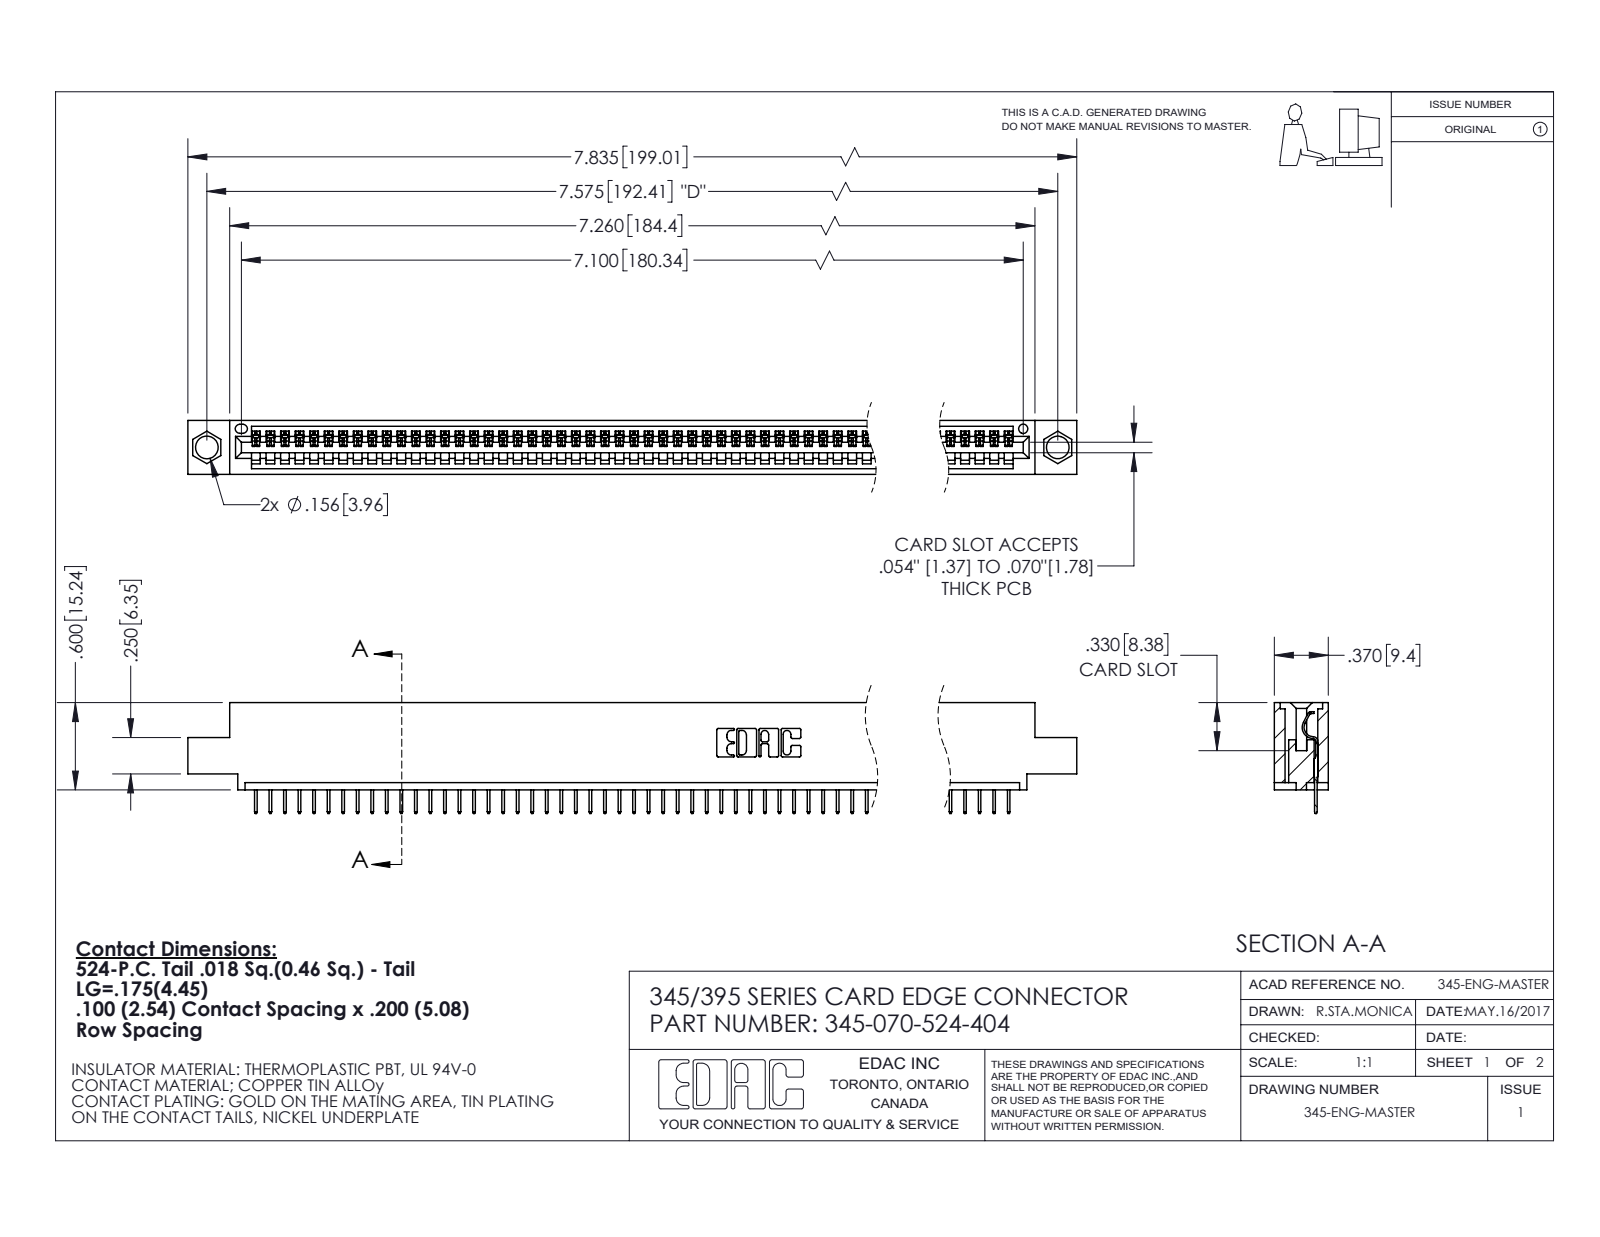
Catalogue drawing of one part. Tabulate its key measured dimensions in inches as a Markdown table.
| quantity | value |
| --- | --- |
| part name | 345-292-001_345-293-124; 345-070-524-404; 345 Part_0.110 Offset - 0.156 Dia-TI |
| STEP written by | SolidWorks 2020 (CONFIG_CONTROL_DESIGN) |
| units | inches |
| bodies | 71 solids, 4484 faces (3318 planar, 1166 cylindrical, 0 other) |
| overall size | 7.835 × 0.762 × 0.37 |
| volume | 1.14 in³ |
| surface area | 37.57 in² |
| round holes (diameter × count) | 0.156 × 2, 0.064 × 1 |
| partial cylindrical surfaces (radius × count) | 0.006 × 140, 0.01 × 22, 0.007 × 6, 0.031 × 6, 0.026 × 3, 0.031 × 2, 0.04 × 2, 0.014 × 1 |
| main face-to-face distances | 0.072, 0.298, 0.37, 0.2, 0.098, 0.272, 0.025, 0.225, 0.072, 0.149 |
| hole center spacings | 0.27, 7.339, 7.575 |
